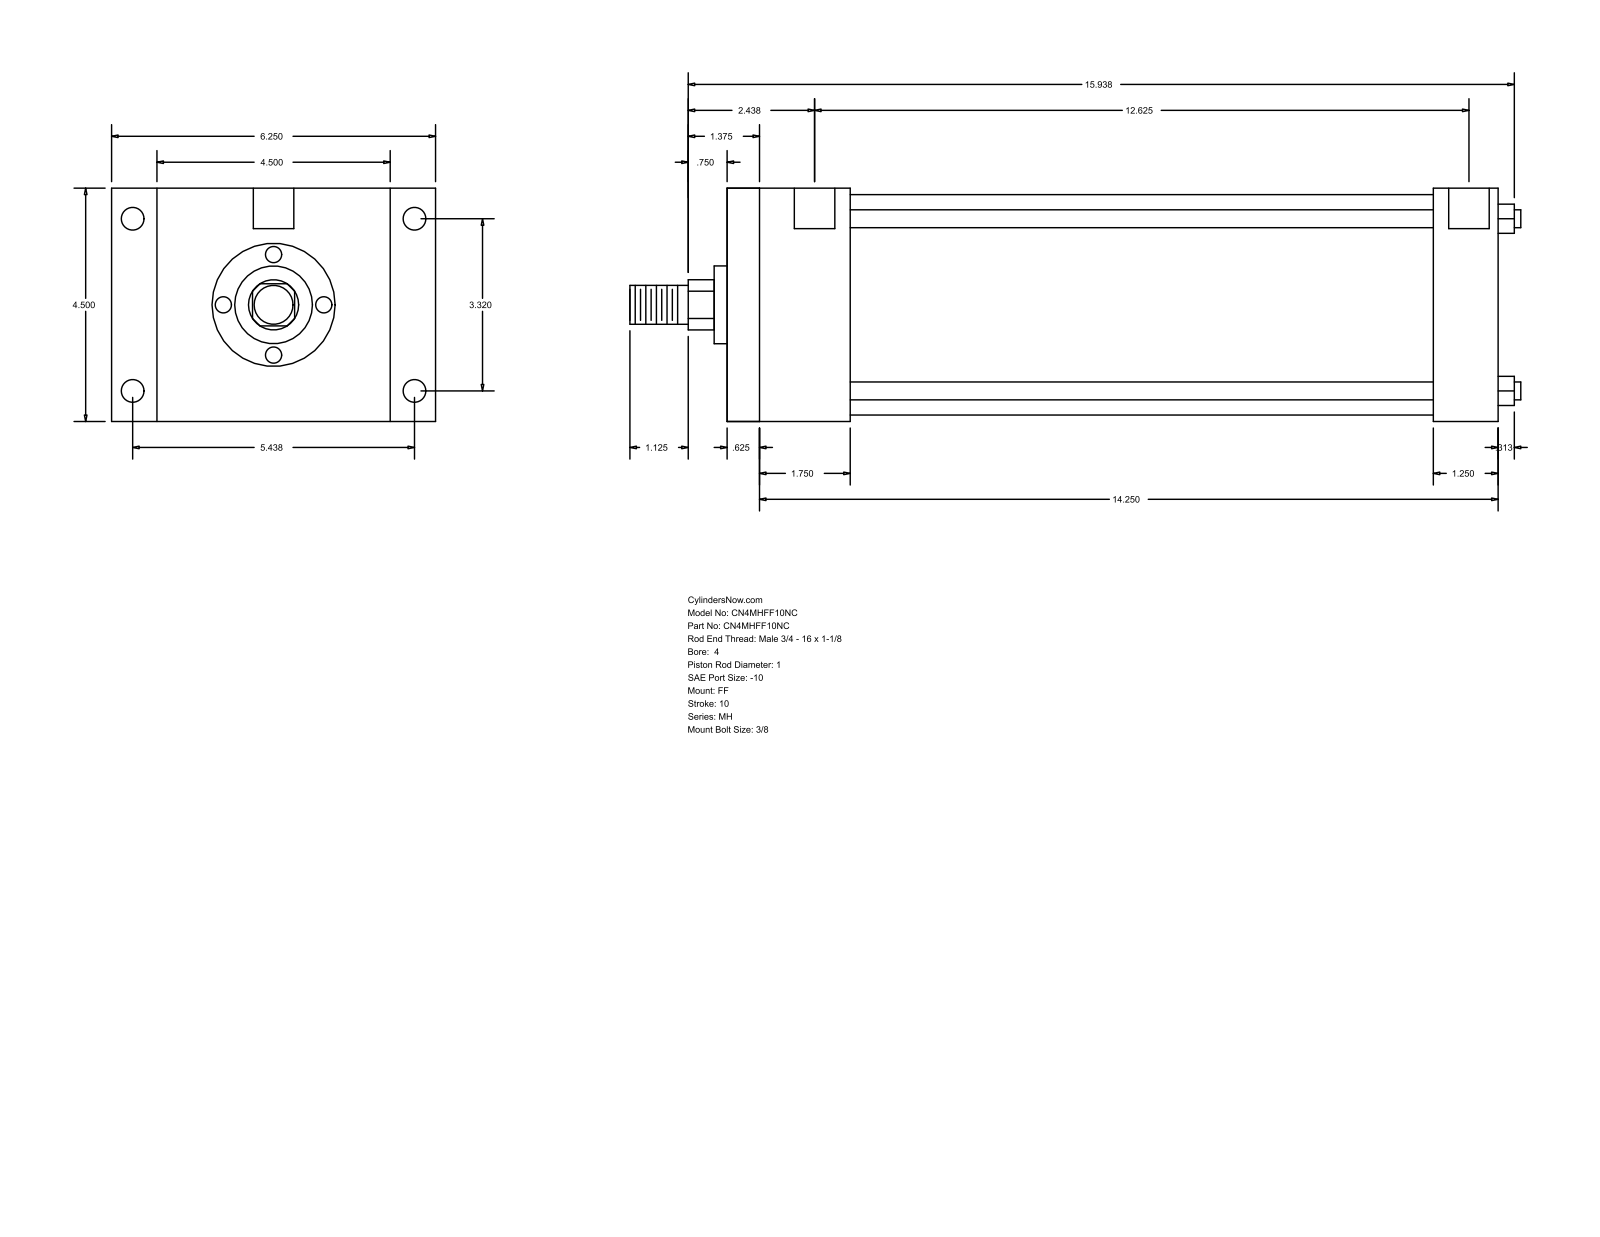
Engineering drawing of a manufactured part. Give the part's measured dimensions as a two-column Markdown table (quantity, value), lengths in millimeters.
| quantity | value |
| --- | --- |
| part name | MH_FF__0400_1 |
| STEP written by | GSSL Pune (CONFIG_CONTROL_DESIGN) |
| units | millimeters |
| bodies | 0 solids, 92 faces (64 planar, 28 cylindrical, 0 other) |
| overall size | 436.56 × 158.75 × 114.3 |
| round holes (diameter × count) | 8.73 × 4, 11.13 × 4, 19.84 × 2 |
| round bosses / shafts (diameter × count) | 8.76 × 4, 107.95 × 1, 38.1 × 1, 25.4 × 1, 19.05 × 1 |
| partial cylindrical surfaces (radius × count) | 12.29 × 1 |
| main face-to-face distances | 114.3, 377.83, 15.87, 361.96, 60.33, 44.46, 317.5, 346.07, 330.2, 285.74 |
| hole center spacings | 84.32, 138.12, 161.82, 323.85, 1.58, 1.59, 320.68, 322.26 |
